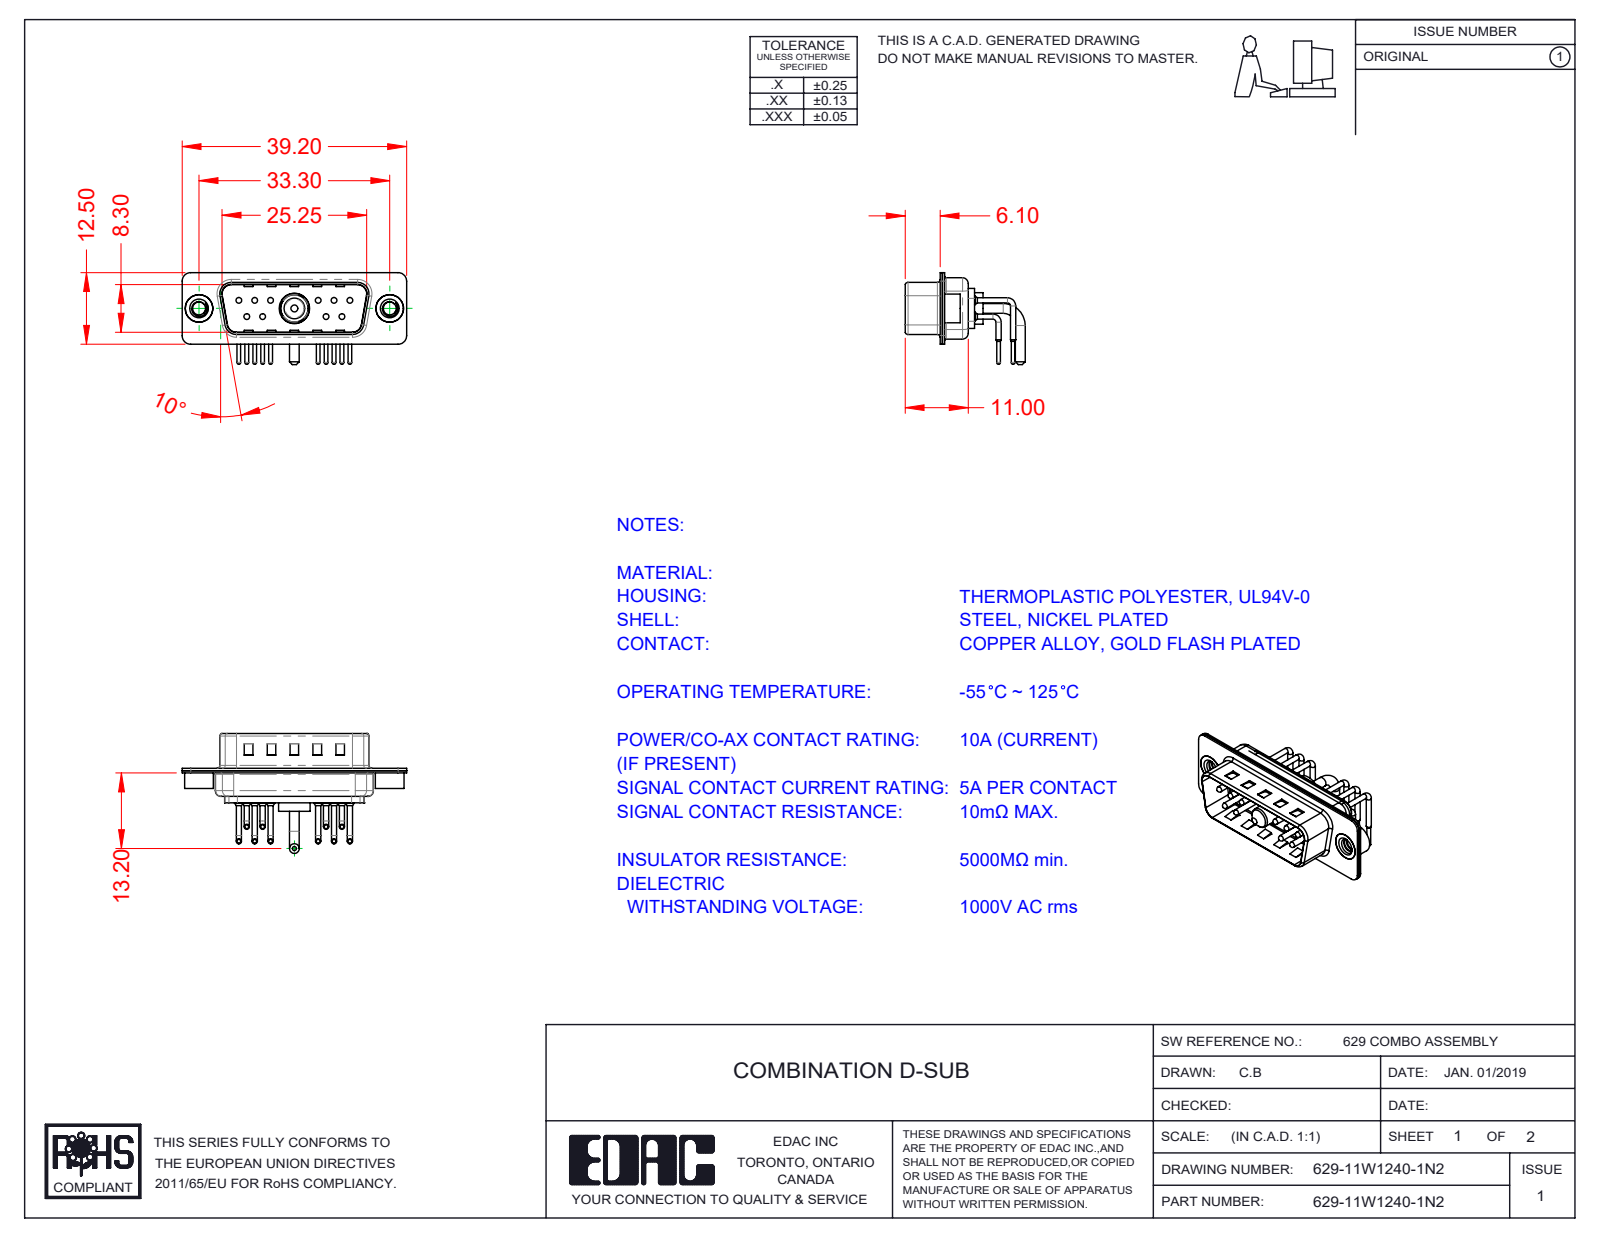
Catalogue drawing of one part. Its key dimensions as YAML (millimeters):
part_name: "629Combo Contact Row 2; 629Combo Threaded Rivet_2; 629Combo Shell Front_15 Contacts; 629Combo Housing_11W1 (+4 more)"
step_written_by: "SolidWorks 2020 (CONFIG_CONTROL_DESIGN)"
units: millimeters
bodies: {solids: 17, faces: 1496, planar: 798, cylindrical: 518, other: 180}
overall_size: [39.2, 20.95, 16.05]
volume: 2006
surface_area: 5183
round_holes:
  - {diameter: 0.75, count: 10}
  - {diameter: 1.6, count: 10}
  - {diameter: 2, count: 10}
  - {diameter: 2.26, count: 2}
  - {diameter: 4, count: 2}
  - {diameter: 4.8, count: 2}
  - {diameter: 4.85, count: 1}
  - {diameter: 5.3, count: 1}
round_bosses_or_shafts:
  - {diameter: 0.9, count: 20}
  - {diameter: 1.5, count: 10}
  - {diameter: 1, count: 10}
  - {diameter: 0.65, count: 10}
  - {diameter: 5, count: 2}
  - {diameter: 4.9, count: 2}
  - {diameter: 1.7, count: 2}
  - {diameter: 5.5, count: 1}
partial_cylinders:
  - {radius: 1.5, count: 16}
  - {radius: 2, count: 12}
  - {radius: 1.01, count: 10}
  - {radius: 0.5, count: 8}
  - {radius: 1.6, count: 8}
  - {radius: 1, count: 7}
  - {radius: 0.25, count: 4}
  - {radius: 0.6, count: 4}
face_to_face_distances: [0.4, 0.8, 9.5, 9.1, 8.7, 9.9, 5.6, 0.75, 1.2, 0.35]
hole_center_spacings: [3.16, 2.77, 13.85, 11.08, 16.62, 5.03, 5.04, 5.54]
